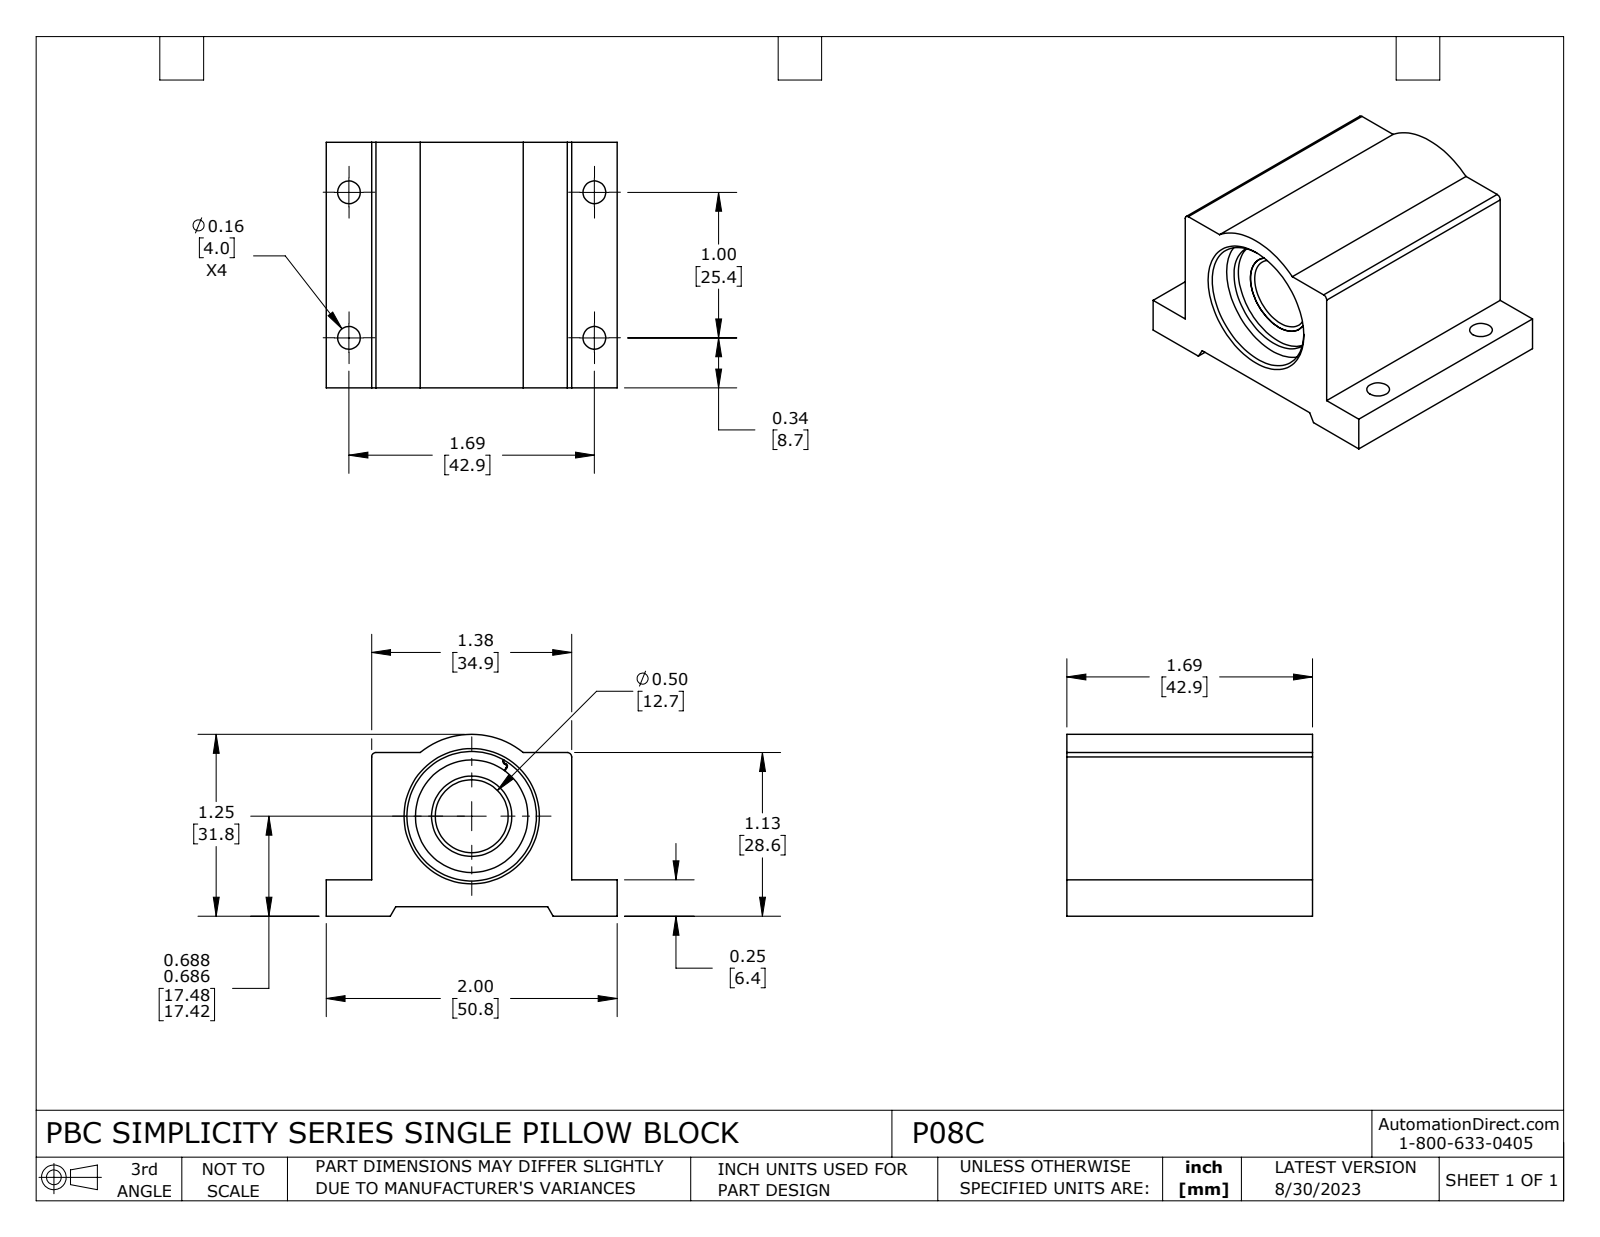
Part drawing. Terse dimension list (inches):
name: P08C
written by: SolidWorks 2021 (CONFIG_CONTROL_DESIGN)
unit: in
bodies: 7 solids, 164 faces (45 planar, 71 cylindrical, 48 other)
size: 2 × 1.688 × 1.25
volume: 2.291 in³; area: 32.35 in²
holes: 4× ⌀0.156, 1× ⌀0.501, 1× ⌀0.552, 1× ⌀0.773, 1× ⌀0.89, 1× ⌀0.931
bosses: 1× ⌀0.943, 1× ⌀0.874, 1× ⌀0.82, 1× ⌀0.712
rounds: 4× R0.014, 2× R0.009, 2× R0.019, 2× R0.03, 1× R0.563
face distances: 1.375, 0.065, 1.06, 1.125, 1.688, 0.25, 0.185, 0.875, 0.313, 1.687
hole spacings: 1, 1.687, 1.961
